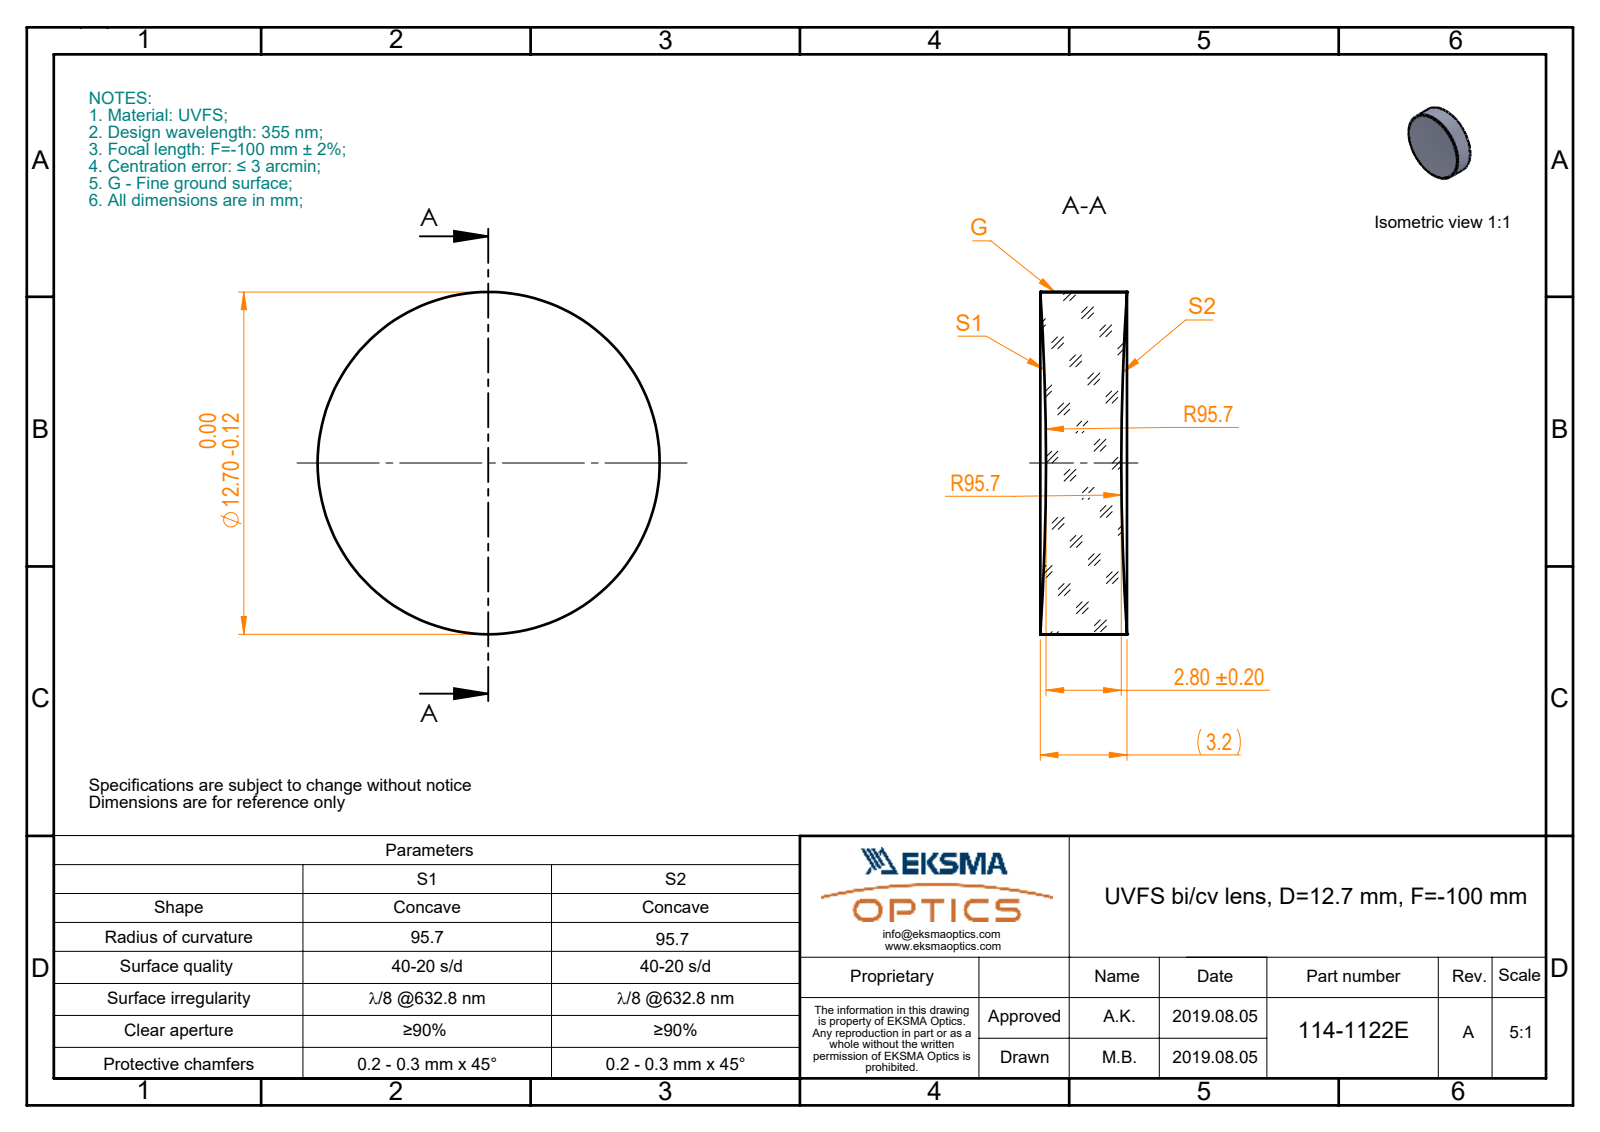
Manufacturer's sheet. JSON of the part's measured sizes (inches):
{"part_name": "114-1122E UVFS bi-cv 12.7 F-100", "step_written_by": "SolidWorks 2017 (CONFIG_CONTROL_DESIGN)", "units": "inches", "bodies": {"solids": 1, "faces": 6, "planar": 0, "cylindrical": 2, "other": 4}, "overall_size": [0.5, 0.5, 0.127], "volume_in3": 0.023, "surface_area_in2": 0.592, "round_bosses_or_shafts": [[0.5, 1]]}
